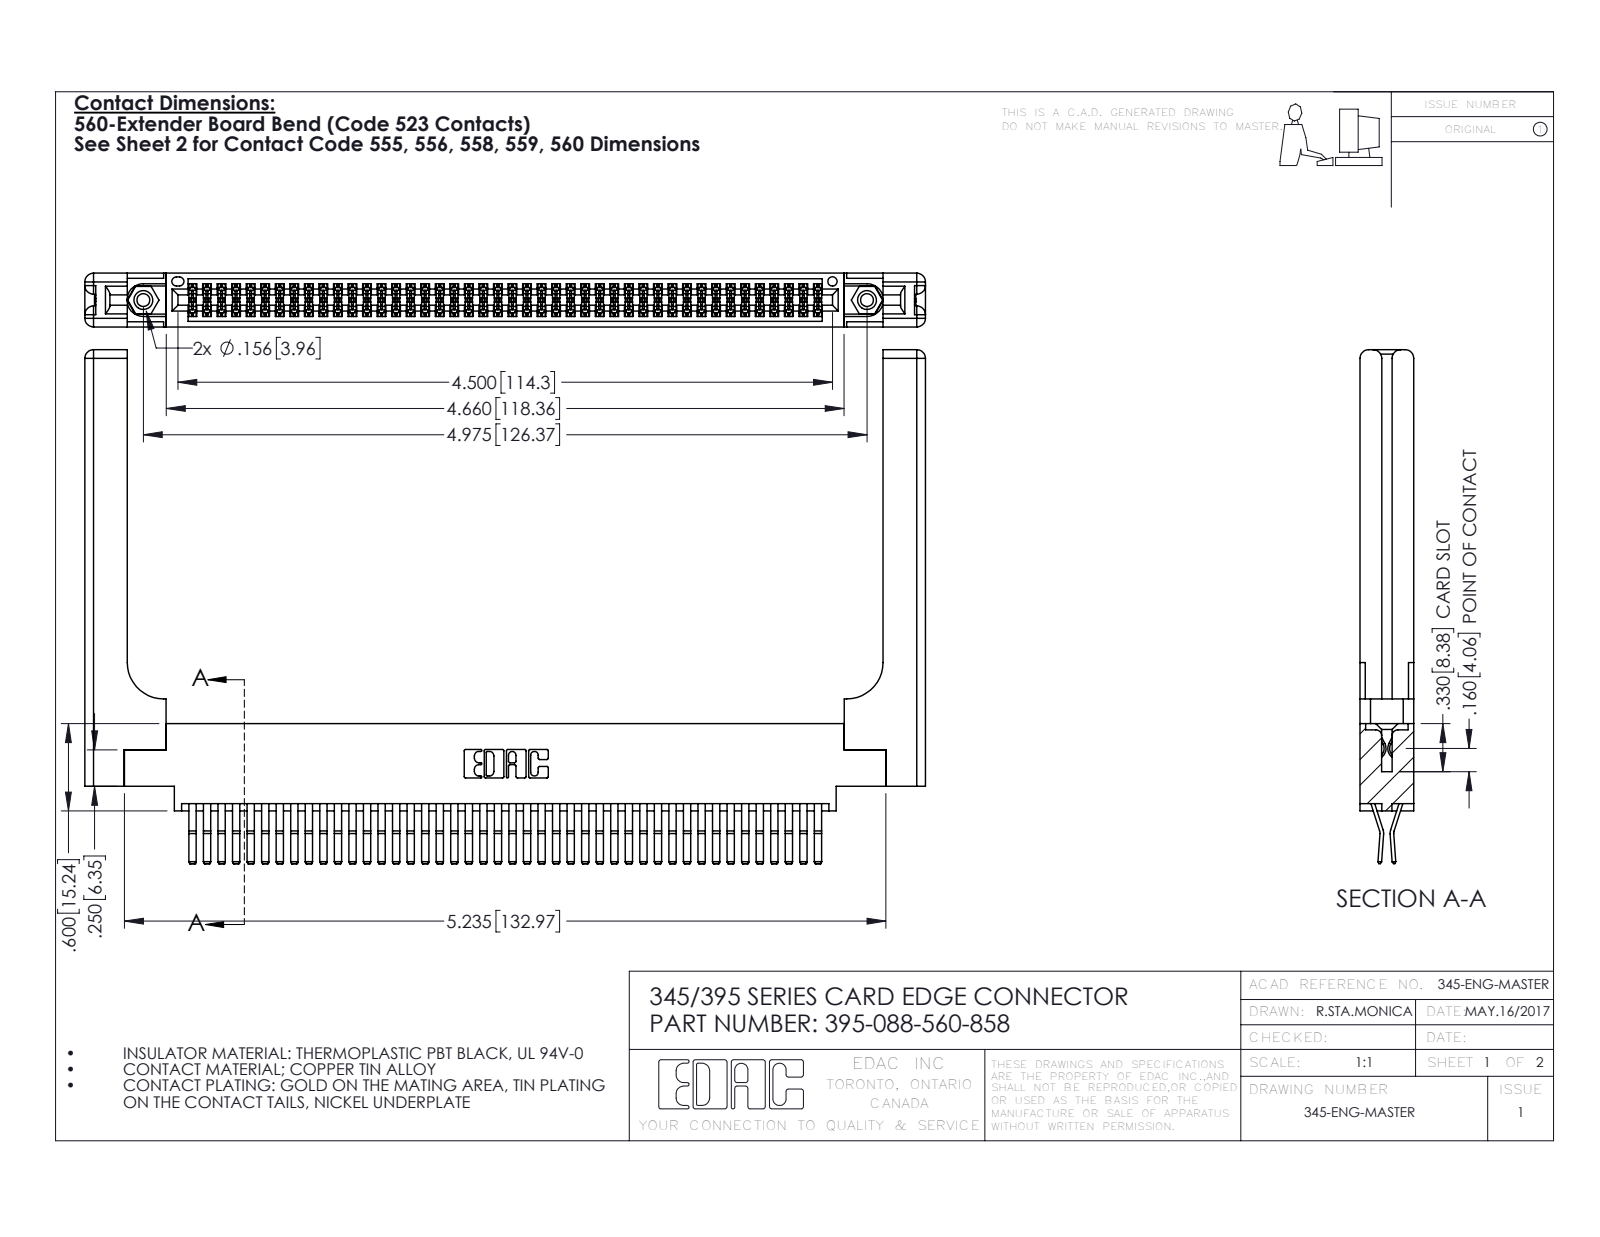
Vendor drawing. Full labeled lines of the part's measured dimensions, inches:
Part name (STEP PRODUCT): 345-292-001_560 Tail; 345-220-058_345-220-058; 345-250-001_345-250-001-102; 395-088-560-858 (+1 more)
STEP written by: SolidWorks 2016 (CONFIG_CONTROL_DESIGN)
Units: inches
Bodies: 93 solids, 4962 faces (3136 planar, 1766 cylindrical, 60 other)
Overall size (bounding box): 5.779 × 3.532 × 0.37
Volume: 1.417 in³ · Surface area: 44.2 in²
Round holes (diameter × count): ⌀0.089 ×2, ⌀0.125 ×2, ⌀0.156 ×2, ⌀0.064 ×1
Round bosses / shafts (diameter × count): ⌀0.155 ×2
Partial cylindrical surfaces — rounded edges, fillets, slot ends (radius × count): R0.006 ×132, R0.01 ×22, R0.06 ×16, R0.007 ×6, R0.031 ×6, R0.026 ×3, R0.01 ×2, R0.014 ×2
Main face-to-face distances: 0.37, 0.072, 0.298, 0.025, 0.098, 0.272, 0.2, 0.225, 0.148, 0.15
Hole centre spacings: 0.27, 4.739, 4.975
